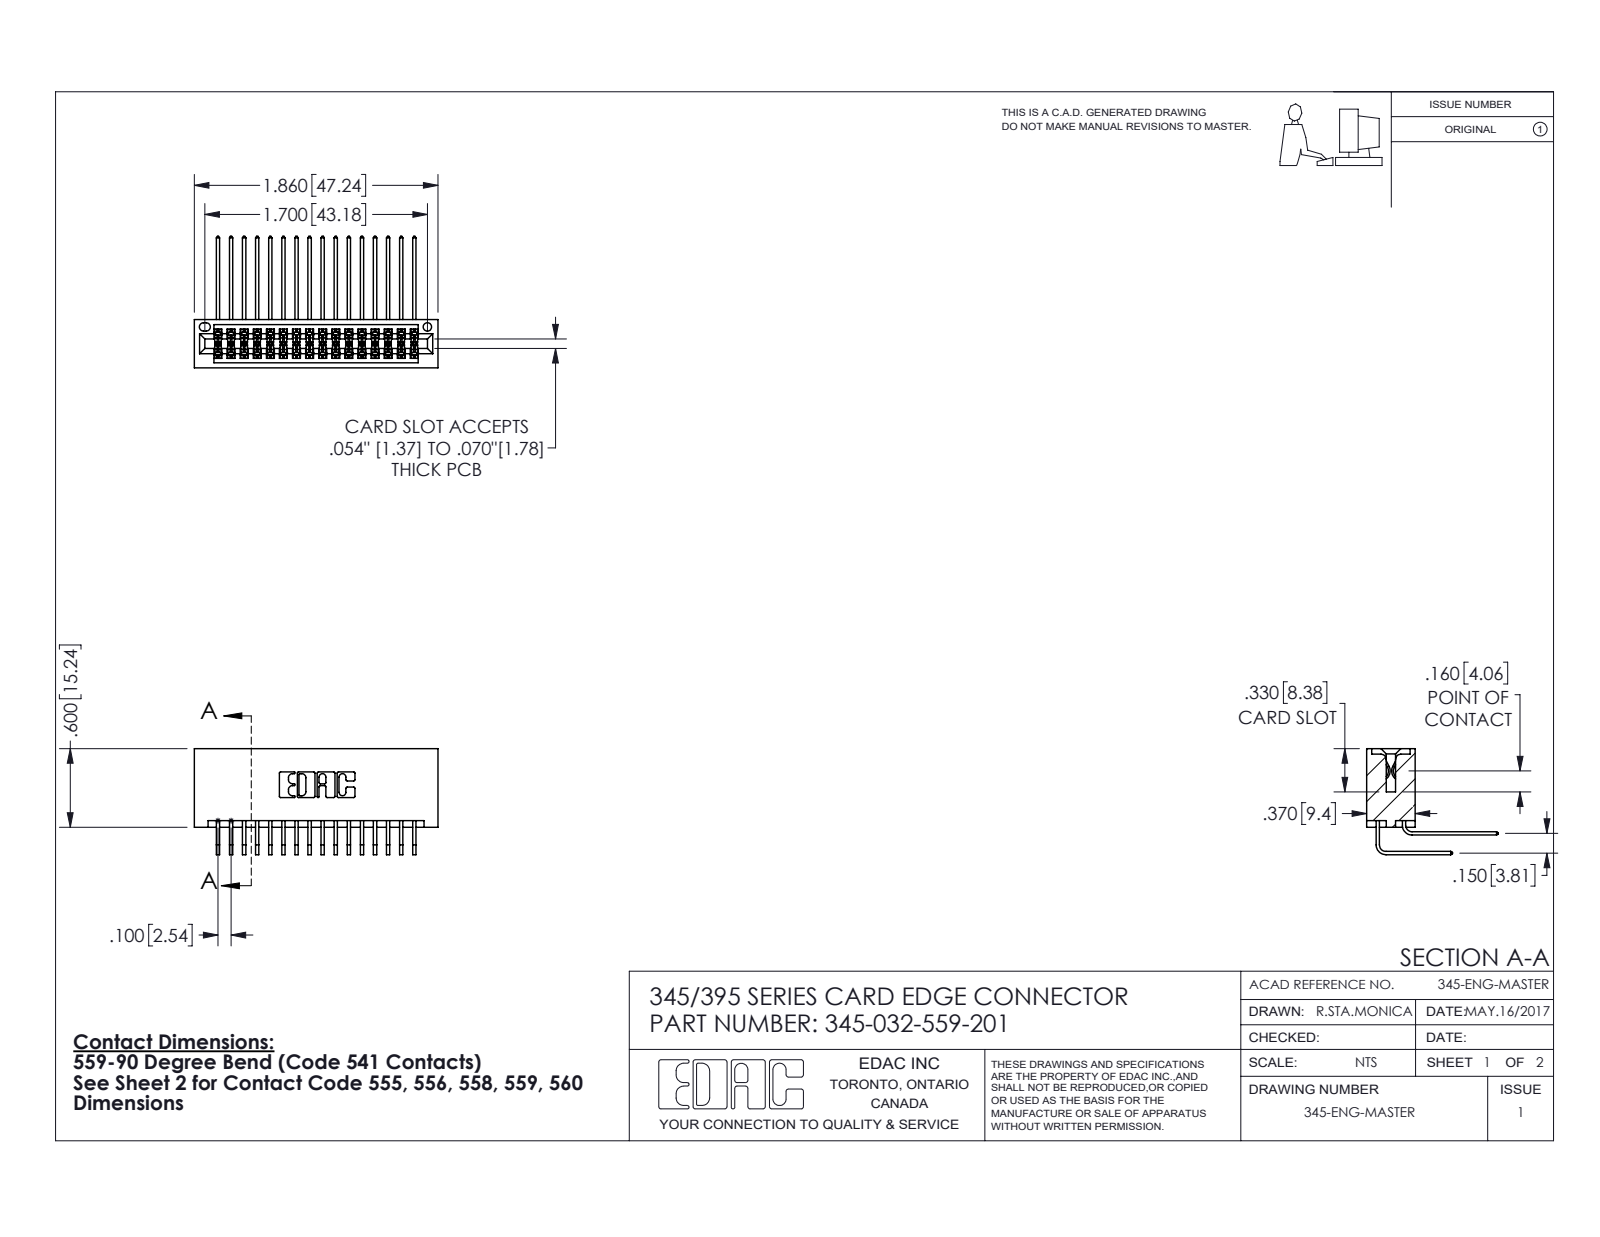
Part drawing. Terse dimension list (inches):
name: 345 Part_No Mounting Lugs; 345-292-001_559 Tail - 2; 345-032-559-201; 345-292-001_558 559 Tail - 1
written by: SolidWorks 2016 (CONFIG_CONTROL_DESIGN)
unit: in
bodies: 33 solids, 1782 faces (1196 planar, 586 cylindrical, 0 other)
size: 1.86 × 1.005 × 0.809
volume: 0.314 in³; area: 12.83 in²
holes: 1× ⌀0.064
rounds: 63× R0.006, 22× R0.01, 6× R0.007, 6× R0.031, 3× R0.026, 2× R0.014, 2× R0.019, 2× R0.022
face distances: 0.072, 0.298, 0.2, 0.37, 0.098, 0.272, 0.025, 0.225, 0.15, 0.175
